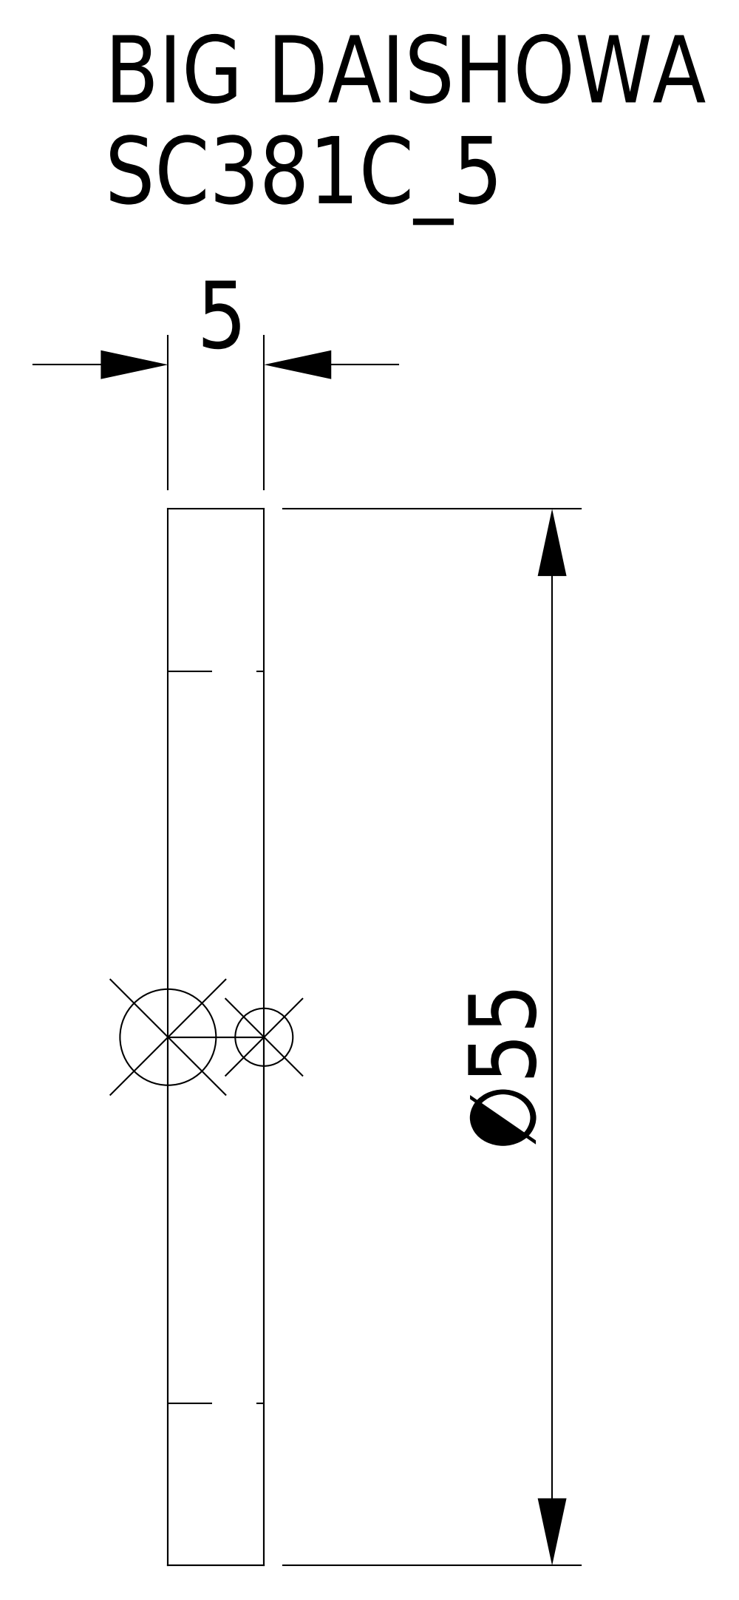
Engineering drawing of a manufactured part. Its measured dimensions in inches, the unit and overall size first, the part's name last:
Units: inches
Overall size (bounding box): 2.165 × 2.165 × 0.197
Round holes (diameter × count): ⌀1.5 ×1
Round bosses / shafts (diameter × count): ⌀2.165 ×1
Main face-to-face distances: 0.197, 0.386
Volume: 0.364 in³ · Surface area: 6.037 in²
Bodies: 1 solid, 8 faces (5 planar, 3 cylindrical, 0 other)
Part name (STEP PRODUCT): SC381C_5
STEP written by: CREO PARAMETRIC BY PTC INC, 2016380 (AUTOMOTIVE_DESIGN)
